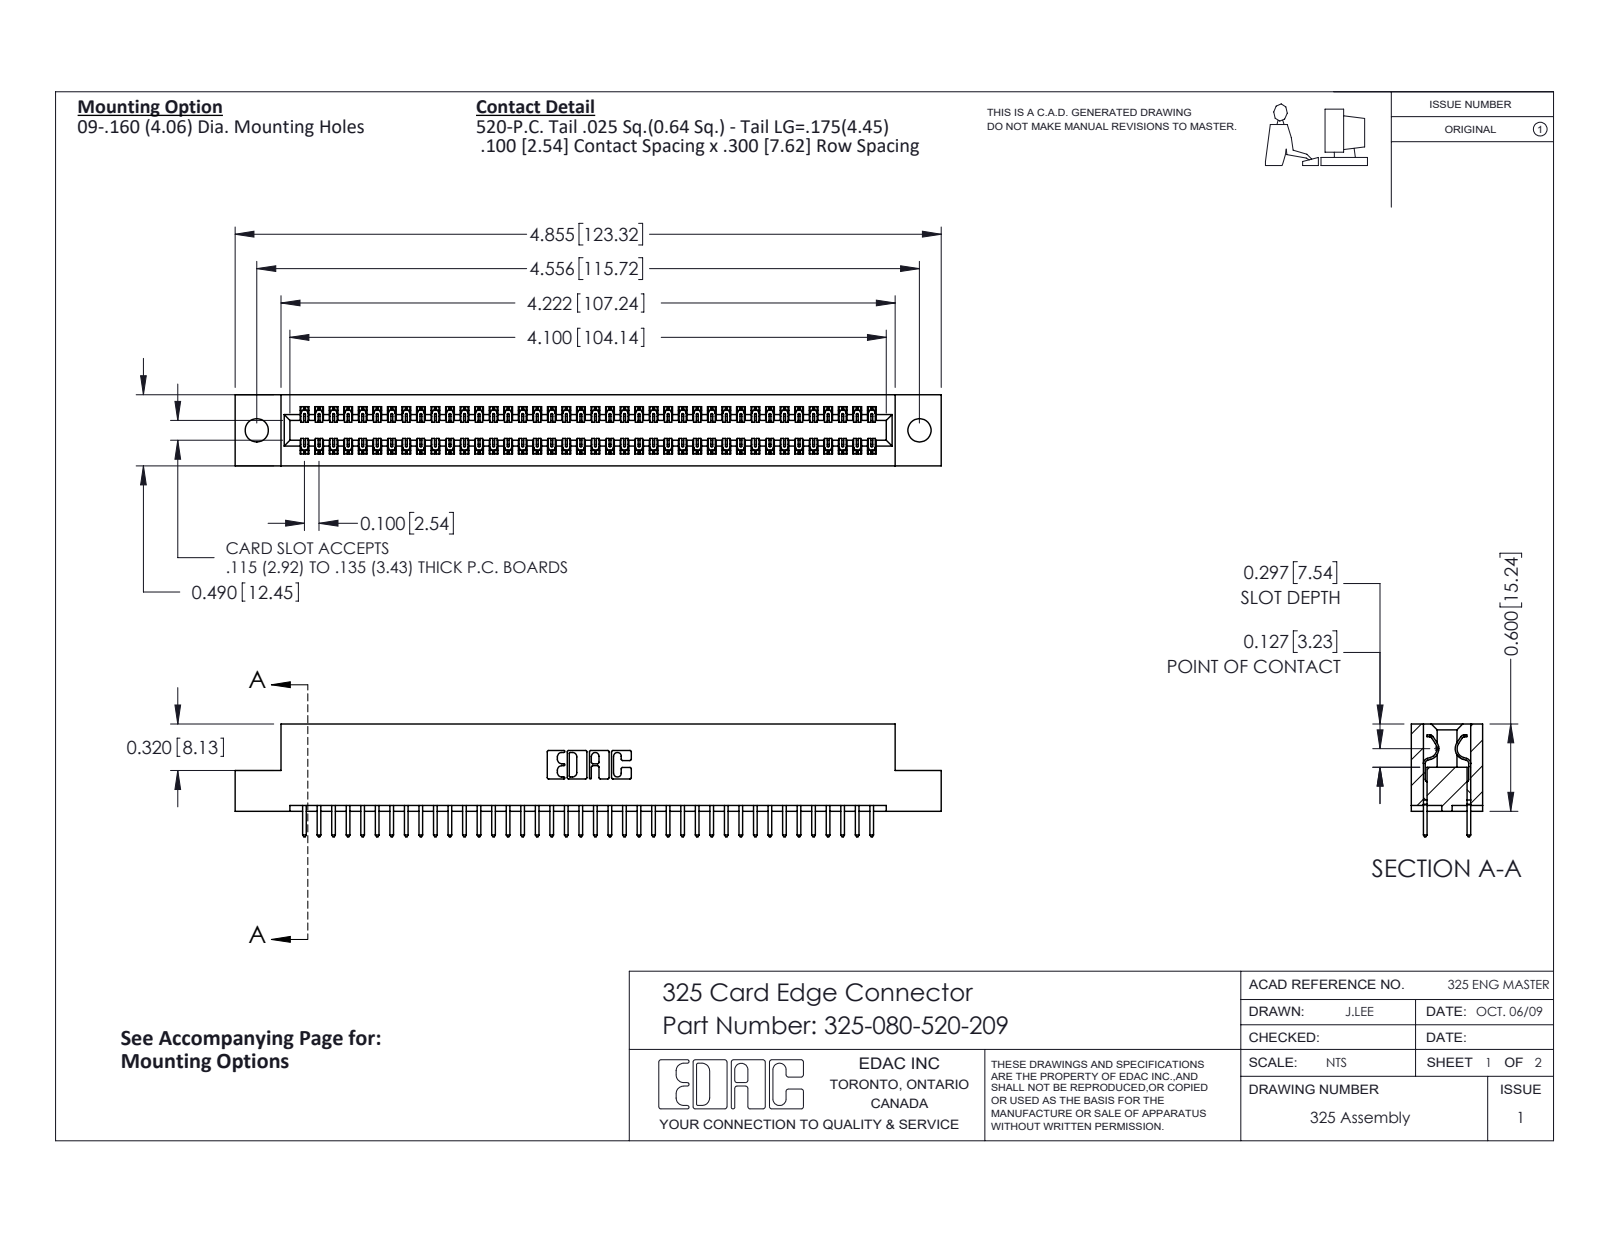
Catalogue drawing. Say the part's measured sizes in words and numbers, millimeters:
The part is named "325-292-001_325-293-120; 325-080-520-209; 325 Part_.160 TH". Its 3-D file was written by "SolidWorks 2016 (CONFIG_CONTROL_DESIGN)". It is 81 solids with 4274 faces: 2950 planar, 1324 cylindrical and 0 other. Overall it measures 123.3 by 19.7 by 12.4 millimeters. Its volume is 15 700 cubic millimeters and its surface area 18 660 square millimeters. Round holes: 2 of diameter 4.1. Partial cylindrical surfaces (rounded edges, fillets, slot ends): 120 of radius 0.2, 80 of radius 0.3, 22 of radius 0.3, 6 of radius 0.2, 6 of radius 0.8, 3 of radius 0.7, 2 of radius 0.4, 2 of radius 0.6. The main face-to-face distances are 2.1, 10.3, 12.4, 7.6, 2.7, 9.7, 0.6, 8.3, 7, 14.2. The hole center spacings are 115.7.
